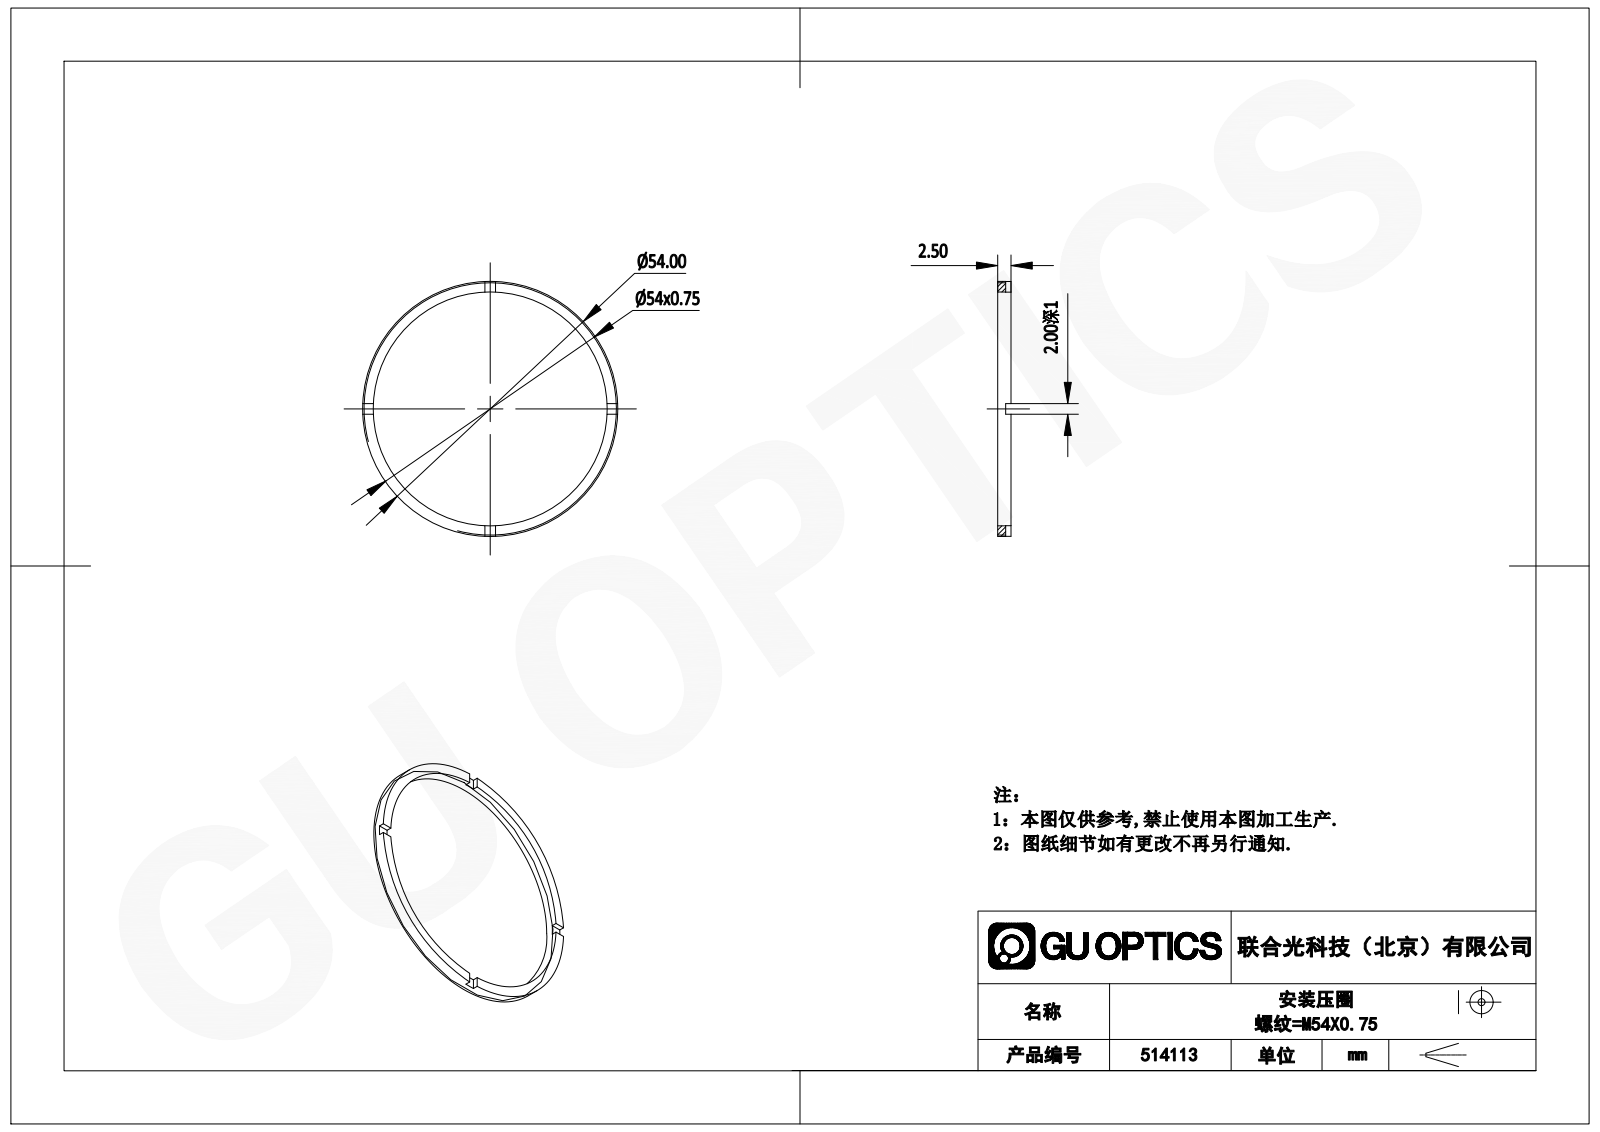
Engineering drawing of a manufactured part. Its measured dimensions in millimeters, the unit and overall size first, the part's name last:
Units: millimetres
Overall size (bounding box): 54 × 54 × 2.5
Round holes (diameter × count): ⌀49 ×1
Round bosses / shafts (diameter × count): ⌀54 ×1
Main face-to-face distances: 2.5, 1.5, 1, 2
Volume: 991 mm³ · Surface area: 1 622 mm²
Bodies: 1 solid, 21 faces (17 planar, 4 cylindrical, 0 other)
Part name (STEP PRODUCT): 514113
STEP written by: SolidWorks 2020 (CONFIG_CONTROL_DESIGN)
